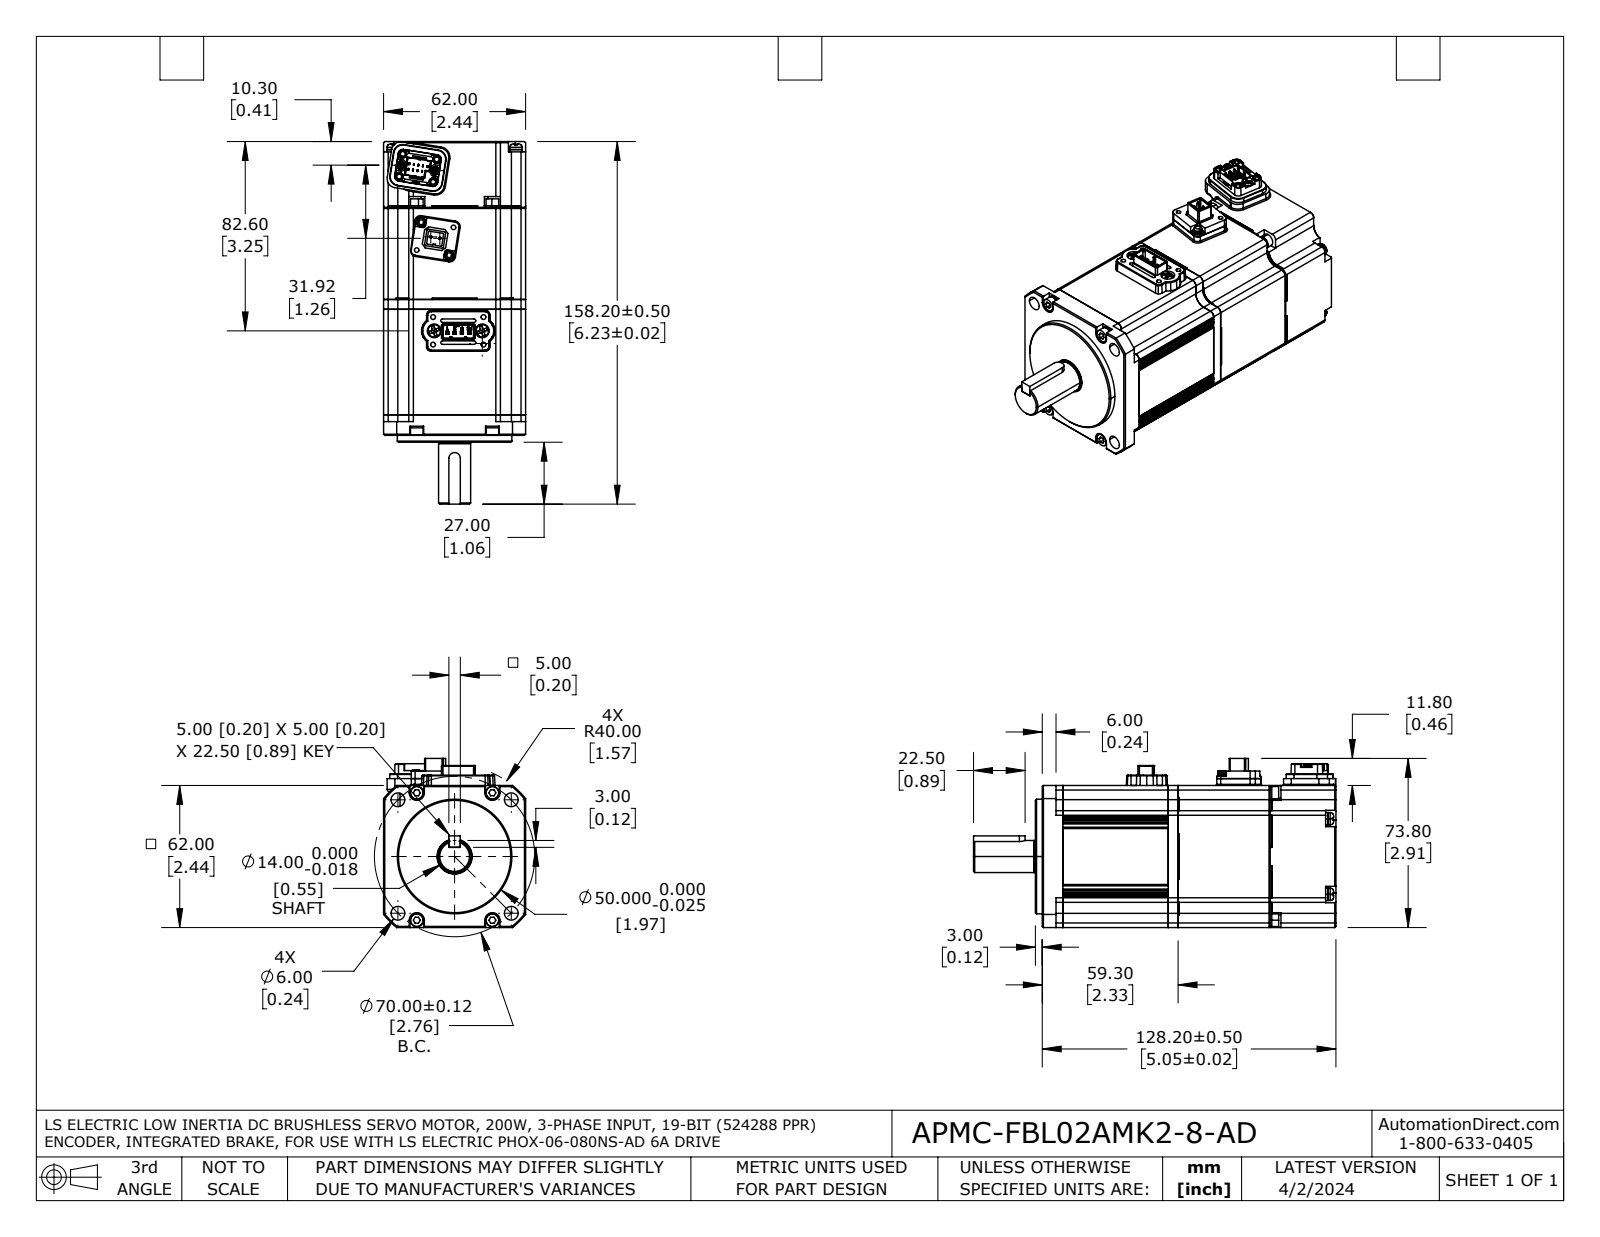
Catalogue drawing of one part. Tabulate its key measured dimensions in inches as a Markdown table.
| quantity | value |
| --- | --- |
| part name | APMC-FBL02AMK2-8-AD |
| STEP written by | SolidWorks 2021 (AUTOMOTIVE_DESIGN) |
| units | inches |
| bodies | 51 solids, 2195 faces (1289 planar, 673 cylindrical, 233 other) |
| overall size | 6.228 × 2.906 × 2.441 |
| volume | 27.4 in³ |
| surface area | 152.9 in² |
| round holes (diameter × count) | 0.083 × 10, 0.138 × 8, 0.118 × 6, 0.236 × 6, 0.079 × 4, 0.122 × 4, 0.039 × 2, 0.13 × 1, 0.134 × 1, 0.512 × 1, 0.602 × 1 |
| round bosses / shafts (diameter × count) | 0.213 × 6, 0.22 × 4, 0.217 × 4, 0.118 × 4, 0.165 × 2, 0.142 × 2, 0.138 × 2, 0.087 × 2 |
| partial cylindrical surfaces (radius × count) | 0.008 × 20, 0.012 × 20, 0.039 × 14, 0.079 × 12, 0.006 × 9, 0.118 × 8, 0.018 × 7, 0.004 × 6 |
| main face-to-face distances | 2.441, 0.169, 0.02, 0.028, 1.811, 1.98, 1.752, 1.583, 3.563, 1.61 |
| hole center spacings | 0.237, 0.335, 0.346, 0.602, 0.63, 0.879, 1.239, 1.273 |
